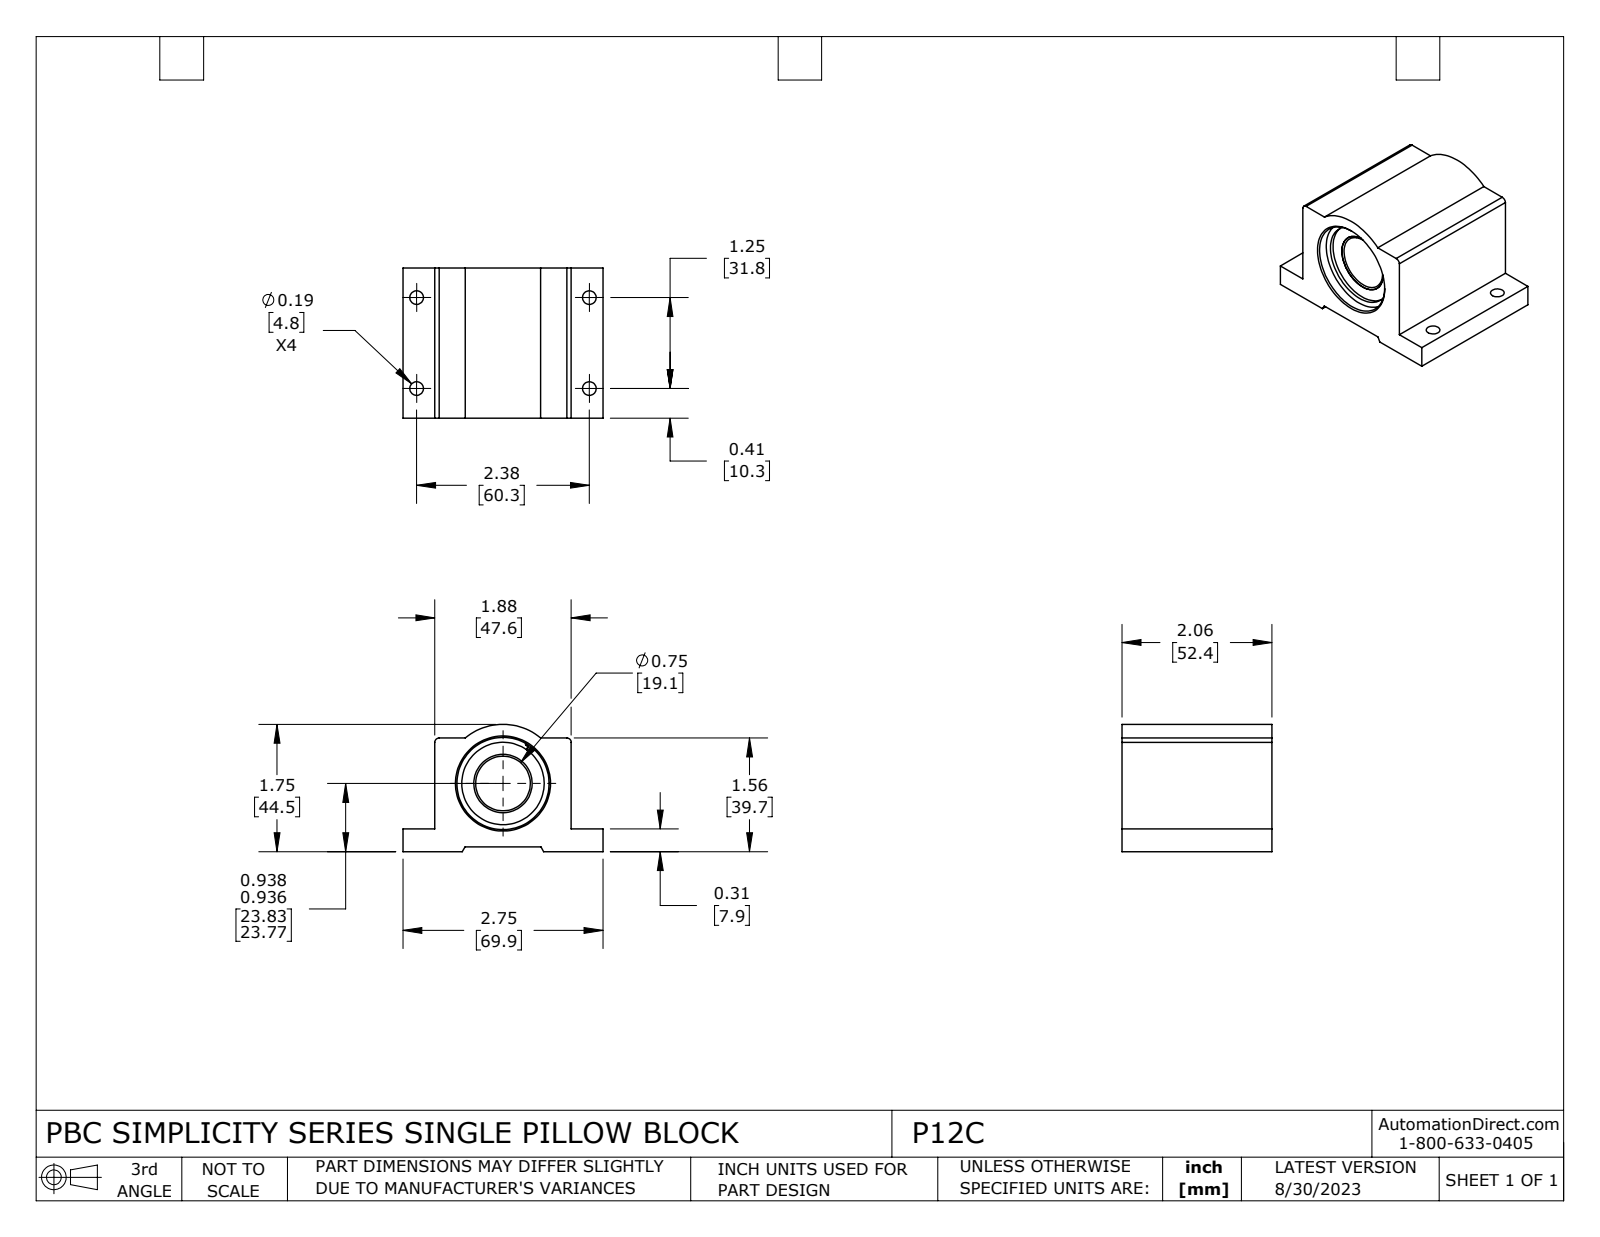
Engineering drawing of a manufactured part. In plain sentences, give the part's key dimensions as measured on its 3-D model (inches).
The part is named "P12C". Its 3-D file was written by "SolidWorks 2021 (CONFIG_CONTROL_DESIGN)". It is 7 solids with 164 faces: 45 planar, 71 cylindrical and 48 other. Overall it measures 2.75 by 2.063 by 1.75 inches. Its volume is 5.368 cubic inches and its surface area 57.16 square inches. Round holes: 4 of diameter 0.187, 1 of diameter 0.751, 1 of diameter 0.802, 1 of diameter 1.133, 1 of diameter 1.267, 1 of diameter 1.33. Round bosses or shafts: 1 of diameter 1.339, 1 of diameter 1.249, 1 of diameter 1.177, 1 of diameter 1.087. Partial cylindrical surfaces (rounded edges, fillets, slot ends): 4 of radius 0.017, 2 of radius 0.012, 2 of radius 0.022, 2 of radius 0.06, 1 of radius 0.813. The main face-to-face distances are 1.875, 0.065, 0.312, 2.062, 0.247, 1.563, 1.498, 1.251, 0.437, 2.312. The hole center spacings are 1.25, 2.375, 2.684.
